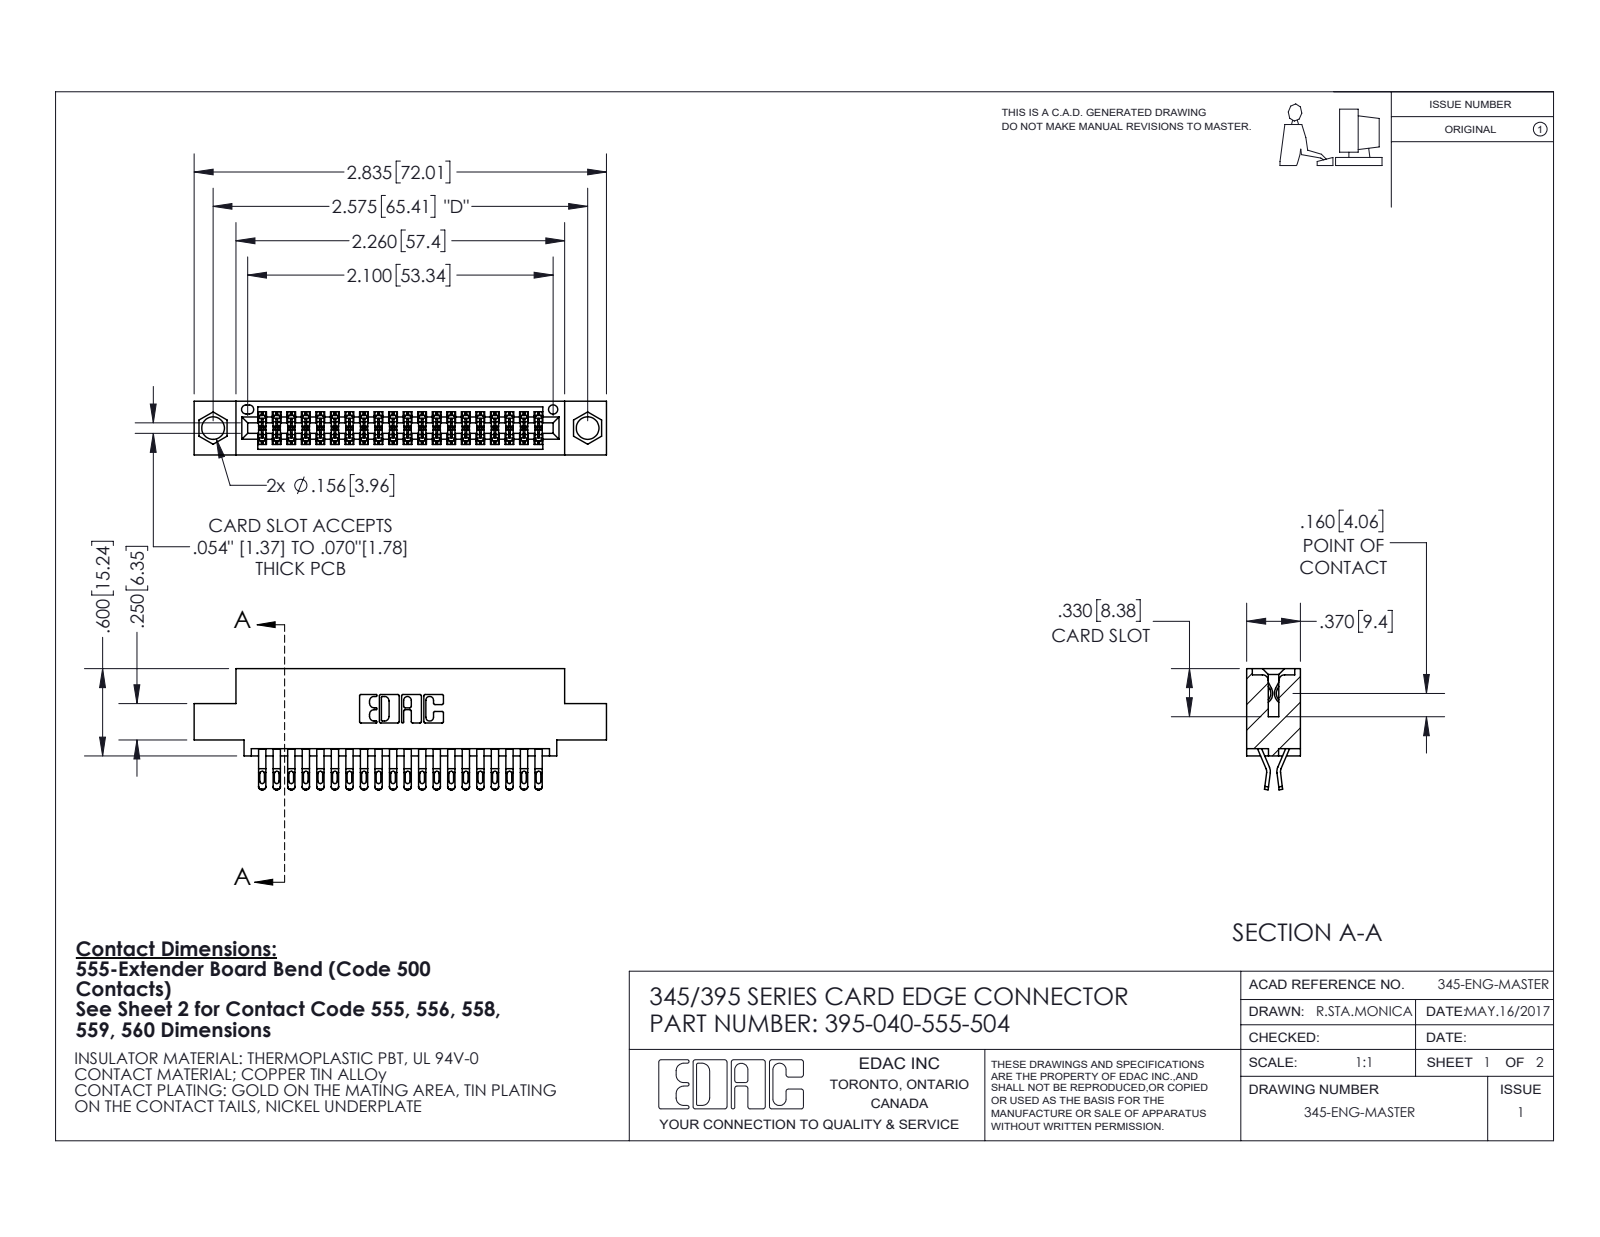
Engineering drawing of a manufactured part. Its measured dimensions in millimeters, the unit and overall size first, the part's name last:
Units: millimetres
Overall size (bounding box): 72 × 21.1 × 9.4
Round holes (diameter × count): ⌀4 ×2, ⌀1.6 ×1
Partial cylindrical surfaces — rounded edges, fillets, slot ends (radius × count): R0.4 ×100, R0.2 ×80, R0.5 ×80, R0.3 ×22, R0.2 ×6, R0.8 ×6, R0.7 ×3, R0.3 ×2
Main face-to-face distances: 7.6, 1.8, 5.1, 9.4, 0.6, 2.5, 6.9, 5.7, 4.4, 3.8
Hole centre spacings: 6.9, 59.5, 65.4
Volume: 6 740 mm³ · Surface area: 9 864 mm²
Bodies: 41 solids, 2384 faces (1338 planar, 1046 cylindrical, 0 other)
Part name (STEP PRODUCT): 395-040-555-504; 345-292-001_555 Tail; 345 Part_0.110 Offset - 0.156 Dia-TI
STEP written by: SolidWorks 2020 (CONFIG_CONTROL_DESIGN)
